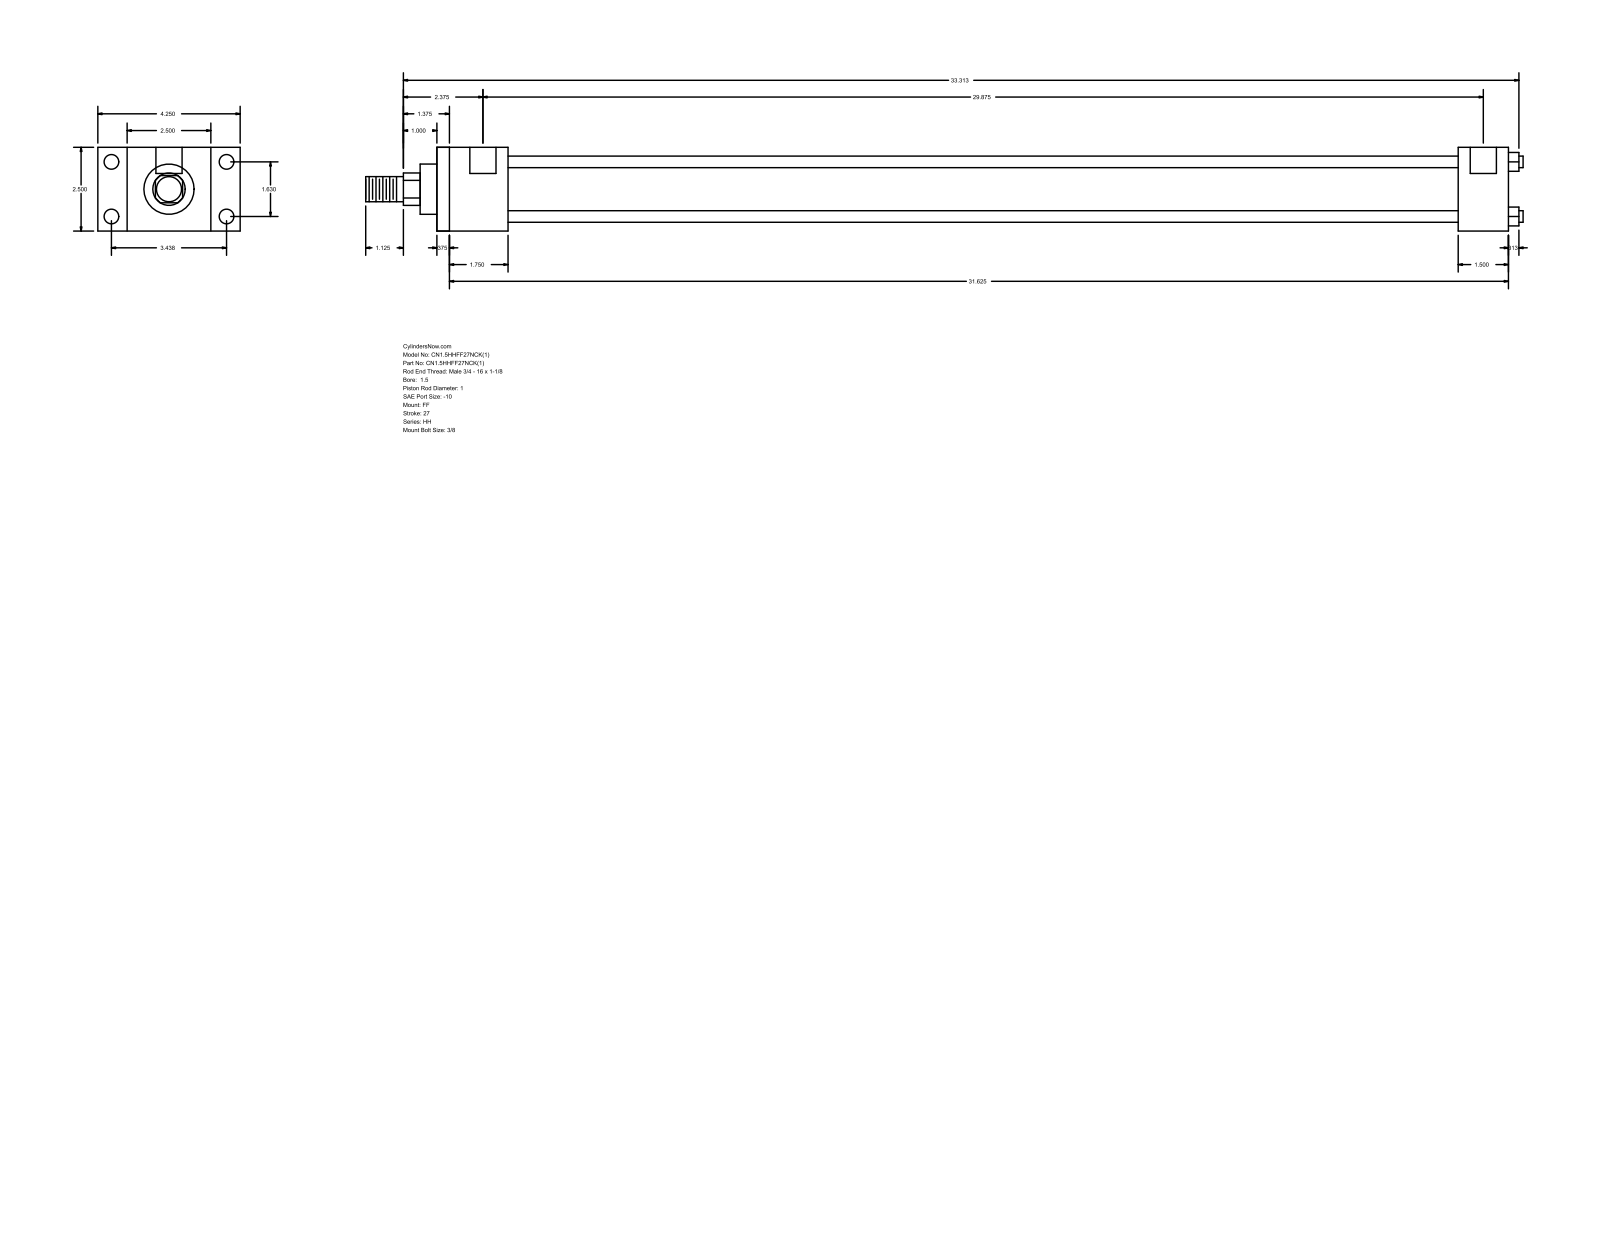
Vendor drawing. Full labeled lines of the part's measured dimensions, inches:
Part name (STEP PRODUCT): HH_FF__0150_1
STEP written by: GSSL Pune (CONFIG_CONTROL_DESIGN)
Units: inches
Bodies: 0 solids, 92 faces (64 planar, 28 cylindrical, 0 other)
Overall size (bounding box): 34.563 × 4.25 × 2.5
Round holes (diameter × count): ⌀0.219 ×4, ⌀0.438 ×4, ⌀0.781 ×2
Round bosses / shafts (diameter × count): ⌀0.345 ×4, ⌀1.75 ×1, ⌀1.5 ×1, ⌀1 ×1, ⌀0.75 ×1
Partial cylindrical surfaces — rounded edges, fillets, slot ends (radius × count): R0.484 ×1
Main face-to-face distances: 2.5, 32, 0.375, 31.625, 1.5, 2.125, 1.75, 29.875, 30.5, 30.125
Hole centre spacings: 0.063, 1.63, 3.438, 3.805, 29.937, 30, 29.875
